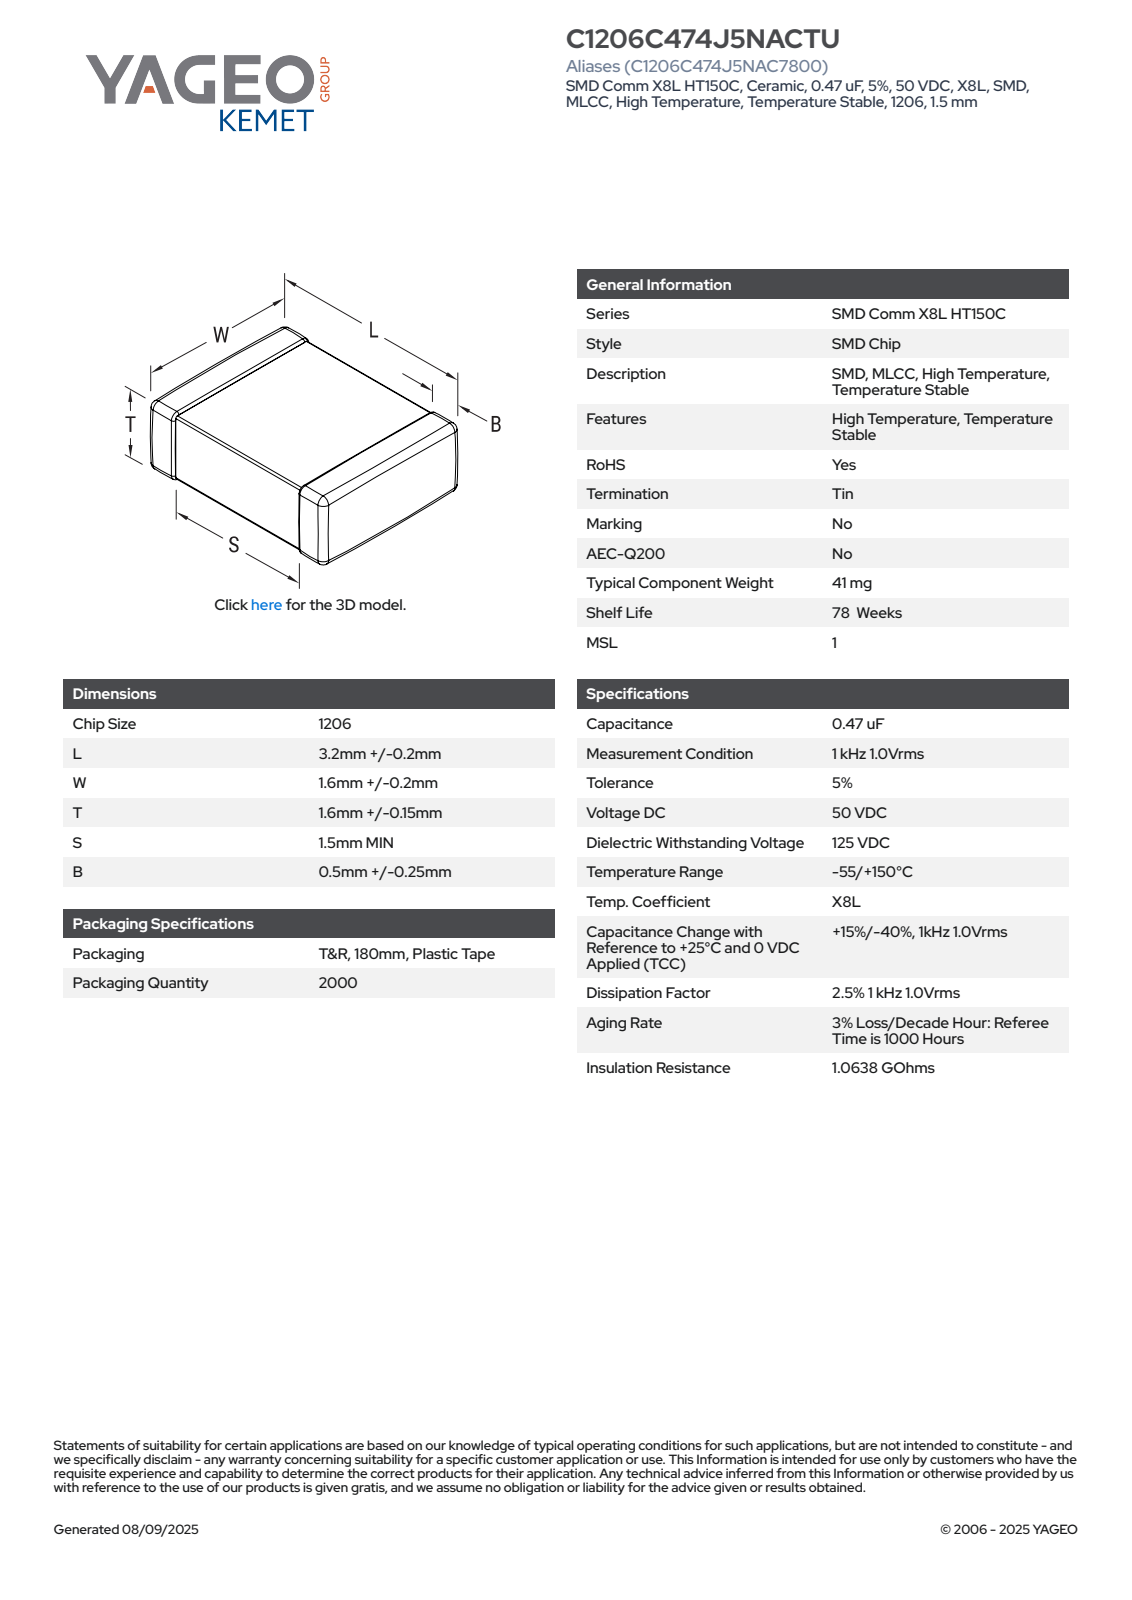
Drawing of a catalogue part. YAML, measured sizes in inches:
part_name: "CCS_CCSTD_1206_L3.4W1.8S1.6T1.75B0.5"
step_written_by: "SolidWorks 2021 (AUTOMOTIVE_DESIGN)"
units: inches
bodies: {solids: 4, faces: 125, planar: 71, cylindrical: 38, other: 16}
overall_size: [0.134, 0.071, 0.069]
volume: 0.001
surface_area: 0.047
face_to_face_distances: [0.067, 0.069, 0.068, 0.066, 0.134, 0.069, 0.071, 0.066, 0.062, 0.072]
